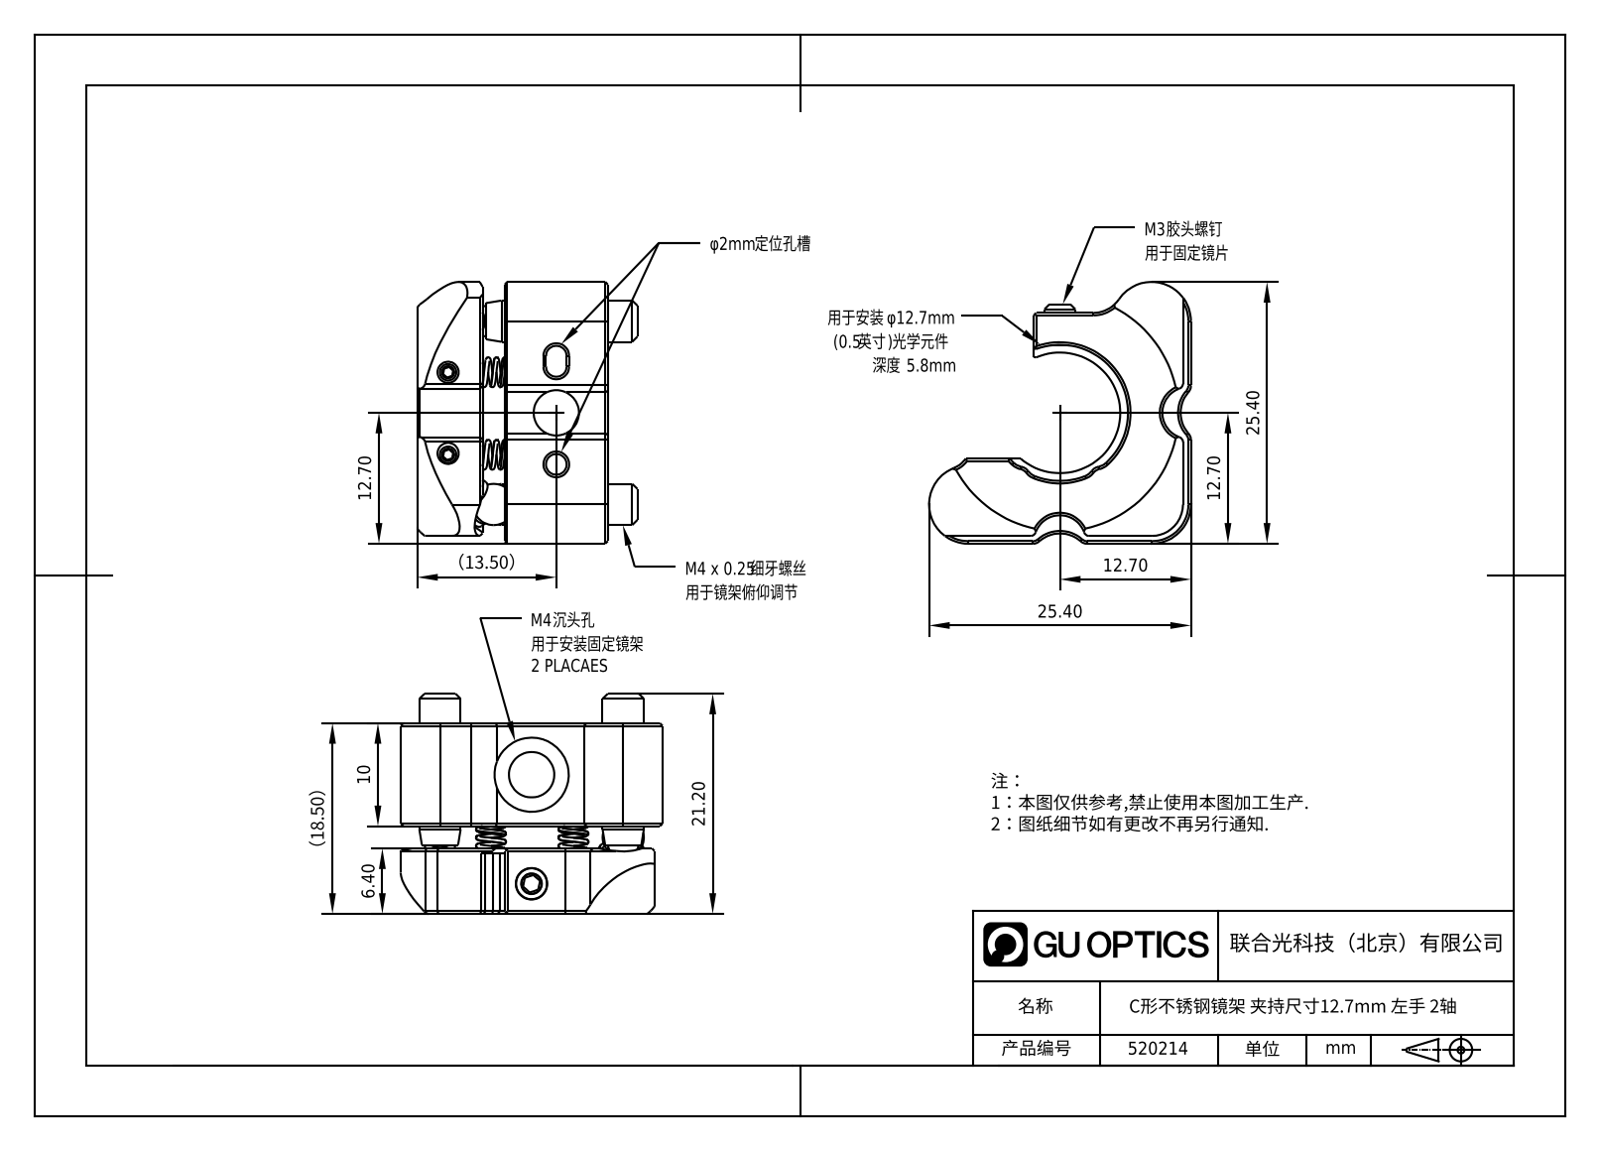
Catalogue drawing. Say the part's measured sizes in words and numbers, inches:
The part is named "520214". Its 3-D file was written by "SolidWorks 2020 (CONFIG_CONTROL_DESIGN)". It is 28 solids with 431 faces: 193 planar, 88 cylindrical and 150 other. Overall it measures 1 by 1 by 0.841 inches. Its volume is 0.237 cubic inches and its surface area 8.703 square inches. Round holes: 4 of diameter 0.063, 4 of diameter 0.126, 4 of diameter 0.134, 2 of diameter 0.079, 2 of diameter 0.118, 2 of diameter 0.148, 2 of diameter 0.171, 2 of diameter 0.173, 2 of diameter 0.283, 1 of diameter 0.098. Round bosses or shafts: 7 of diameter 0.079, 6 of diameter 0.102, 2 of diameter 0.157, 2 of diameter 0.059, 1 of diameter 0.118. Partial cylindrical surfaces (rounded edges, fillets, slot ends): 8 of radius 0.039, 5 of radius 0.15, 4 of radius 0.02, 4 of radius 0.059, 3 of radius 0.098, 3 of radius 0.118, 2 of radius 0.045, 2 of radius 0.197. The main face-to-face distances are 0.394, 0.335, 0.728, 0.25, 0.085, 0.478, 0.079, 0.221, 0.02, 0.3. The hole center spacings are 0.31, 0.441, 0.195, 0.197, 0.31, 0.415, 0.505, 0.542.
